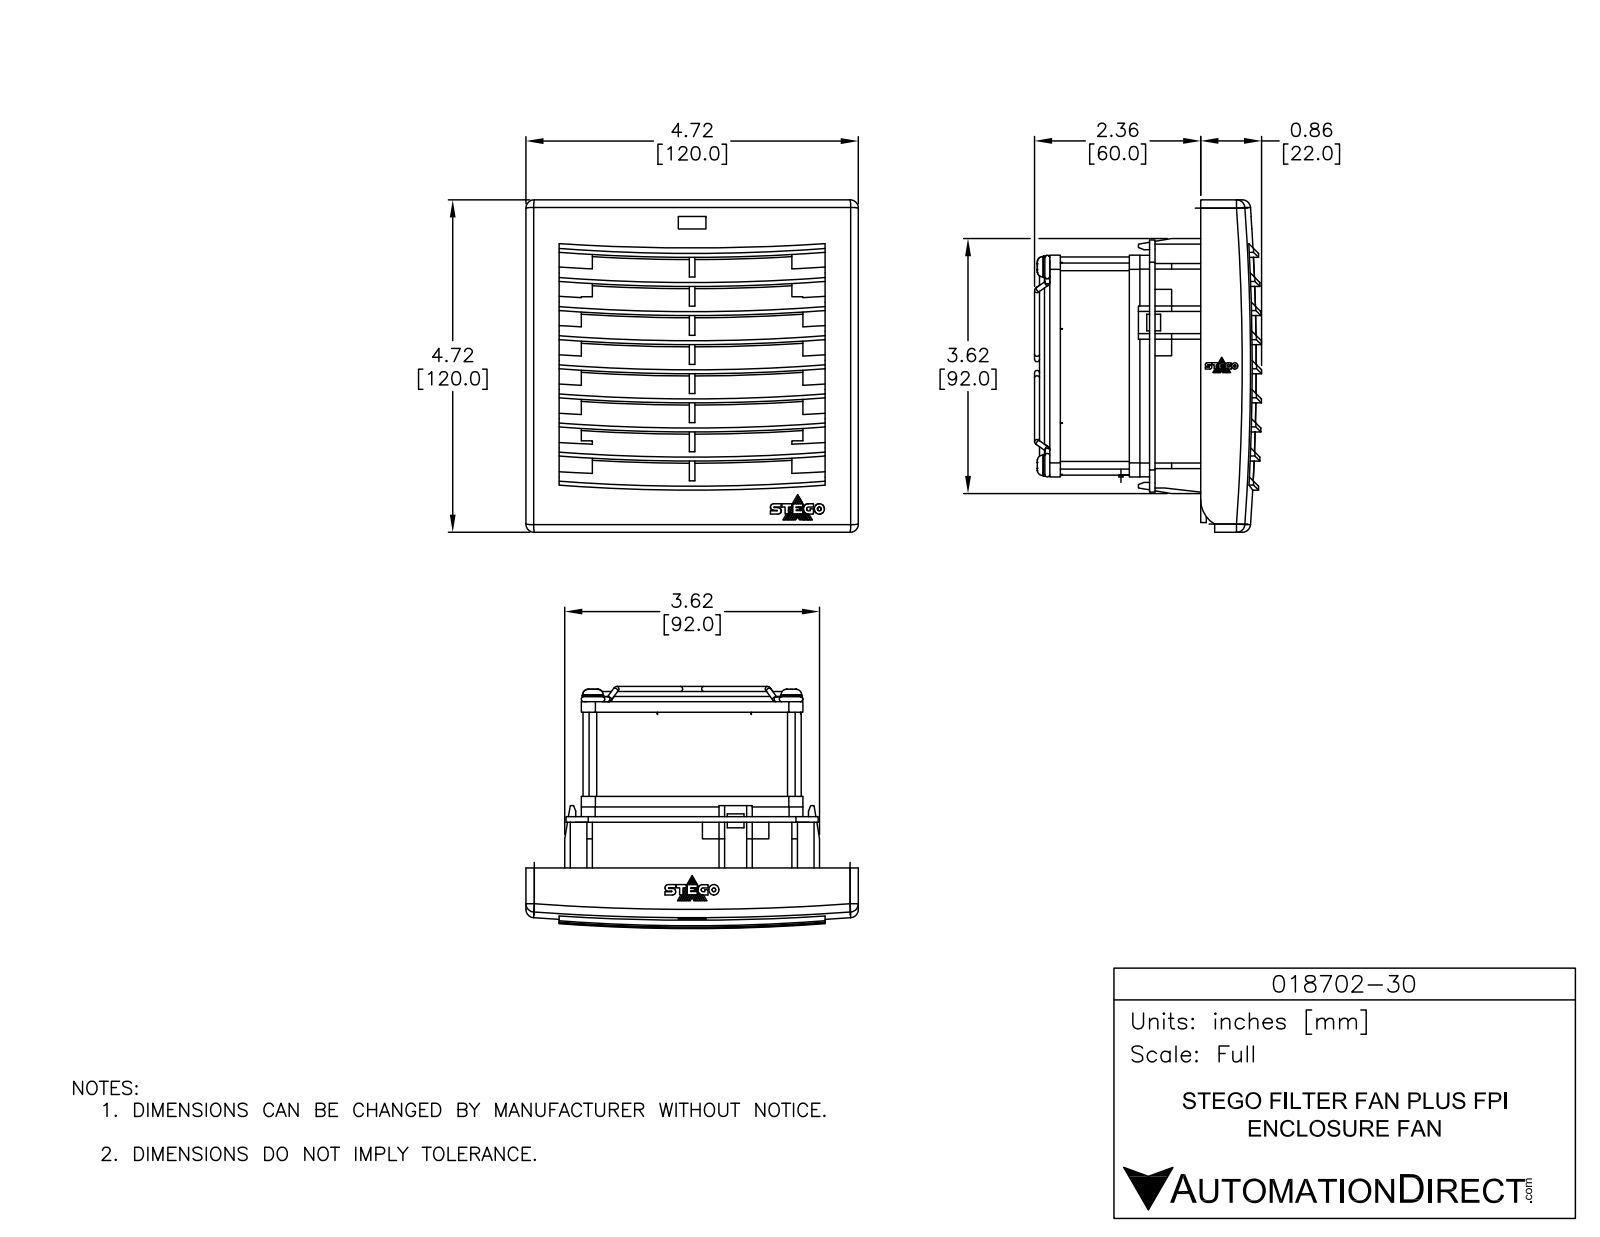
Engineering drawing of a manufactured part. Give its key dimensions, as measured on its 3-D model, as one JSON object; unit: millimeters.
{"part_name": "018702-30", "step_written_by": "SolidWorks 2018 (AUTOMOTIVE_DESIGN)", "units": "millimeters", "bodies": {"solids": 21, "faces": 667, "planar": 322, "cylindrical": 186, "other": 159}, "overall_size": [120, 120, 81.8], "volume_mm3": 253800, "surface_area_mm2": 135200, "round_holes": [[4.4, 2], [4.4, 2], [75.6, 1]], "round_bosses_or_shafts": [[1.8, 12], [7.8, 4], [2.9, 4], [78.7, 1], [46.9, 1]], "partial_cylinders_radius": [[0.6, 40], [0.2, 20], [31.4, 14], [0.2, 7], [31.4, 7], [1.4, 4], [1.7, 4], [3.2, 4]], "face_to_face_distances": [7.4, 2, 14.9, 22.3, 18.5, 29.7, 102, 18, 3.6, 3.8], "hole_center_spacings": [71.6, 50.6, 101.3, 50.6, 50.6]}
